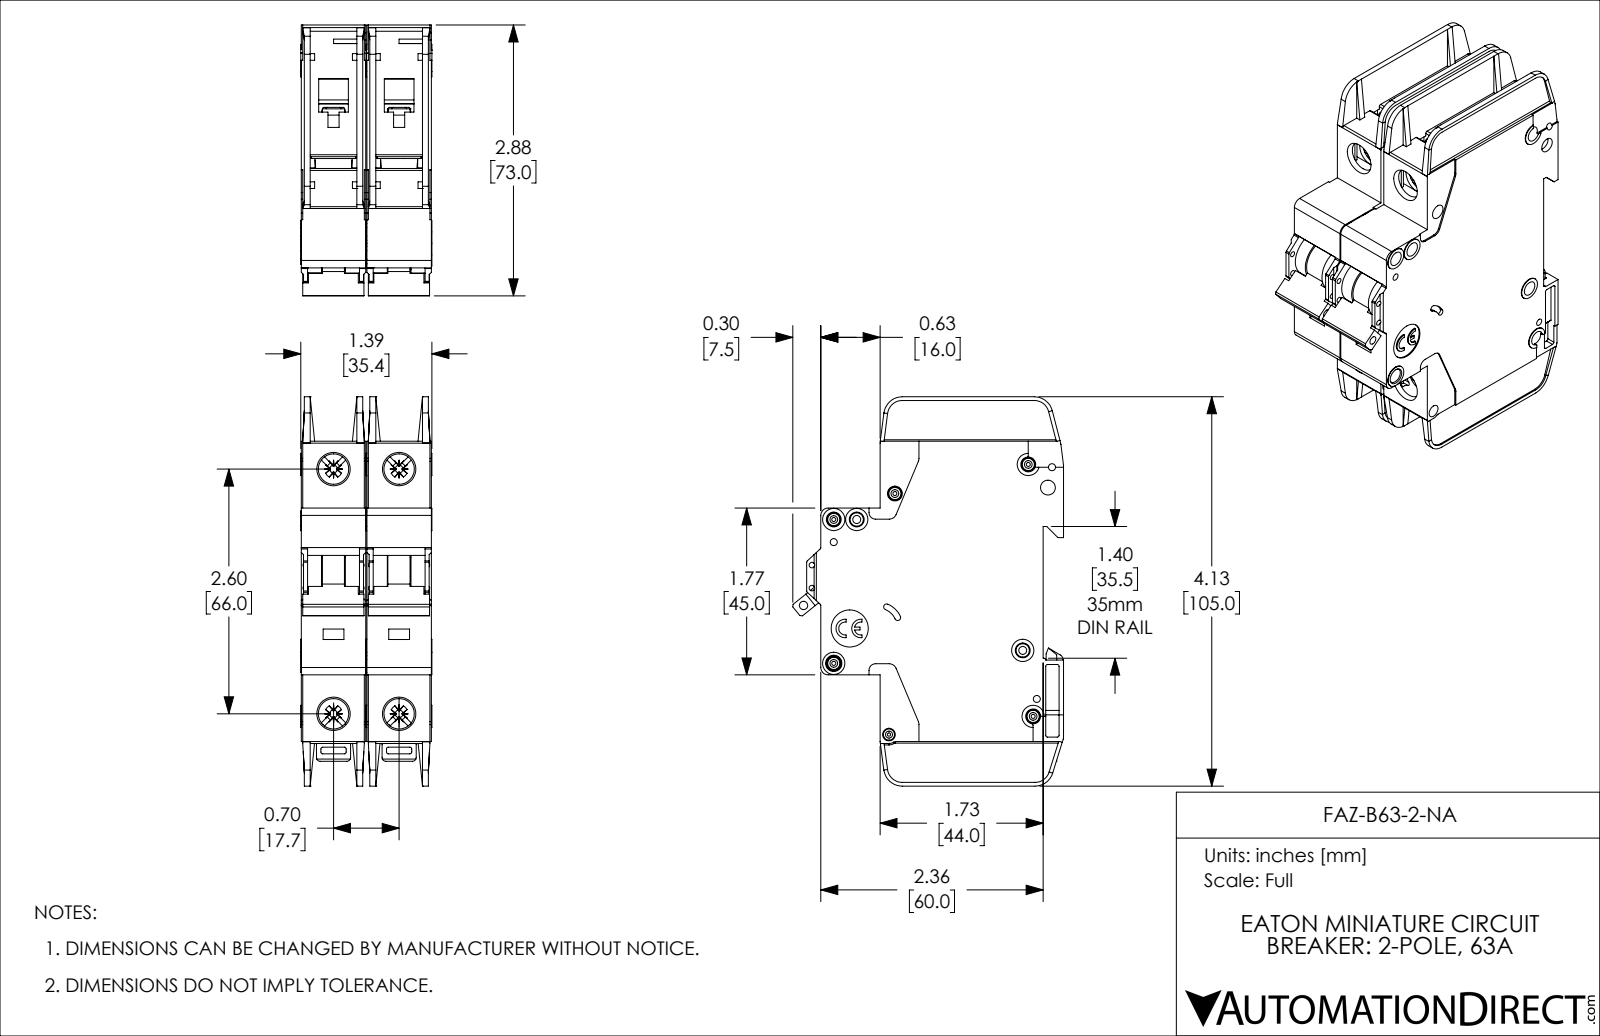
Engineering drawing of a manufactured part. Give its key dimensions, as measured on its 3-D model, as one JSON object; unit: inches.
{"part_name": "FAZ-B63-2-NA", "step_written_by": "SolidWorks 2019 (AUTOMOTIVE_DESIGN)", "units": "inches", "bodies": {"solids": 2, "faces": 2254, "planar": 1342, "cylindrical": 714, "other": 198}, "overall_size": [4.134, 2.876, 1.394], "volume_in3": 9.365, "surface_area_in2": 82.01, "round_holes": [[0.157, 8], [0.043, 5], [0.075, 4], [0.323, 4], [0.059, 2], [0.085, 2], [0.035, 1], [0.089, 1], [0.098, 1], [0.134, 1], [0.394, 1]], "round_bosses_or_shafts": [[0.13, 5], [0.236, 4], [0.118, 3], [0.098, 2]], "partial_cylinders_radius": [[0.02, 57], [0.016, 20], [0.039, 14], [0.079, 10], [0.043, 8], [0.008, 5], [0.197, 5], [0.01, 4]], "face_to_face_distances": [0.697, 0.047, 0.685, 0.591, 0.094, 0.638, 0.543, 1.382, 0.744, 0.65], "hole_center_spacings": [0.244, 0.537, 0.697, 0.87, 2.598, 2.69, 0.189, 0.199]}
